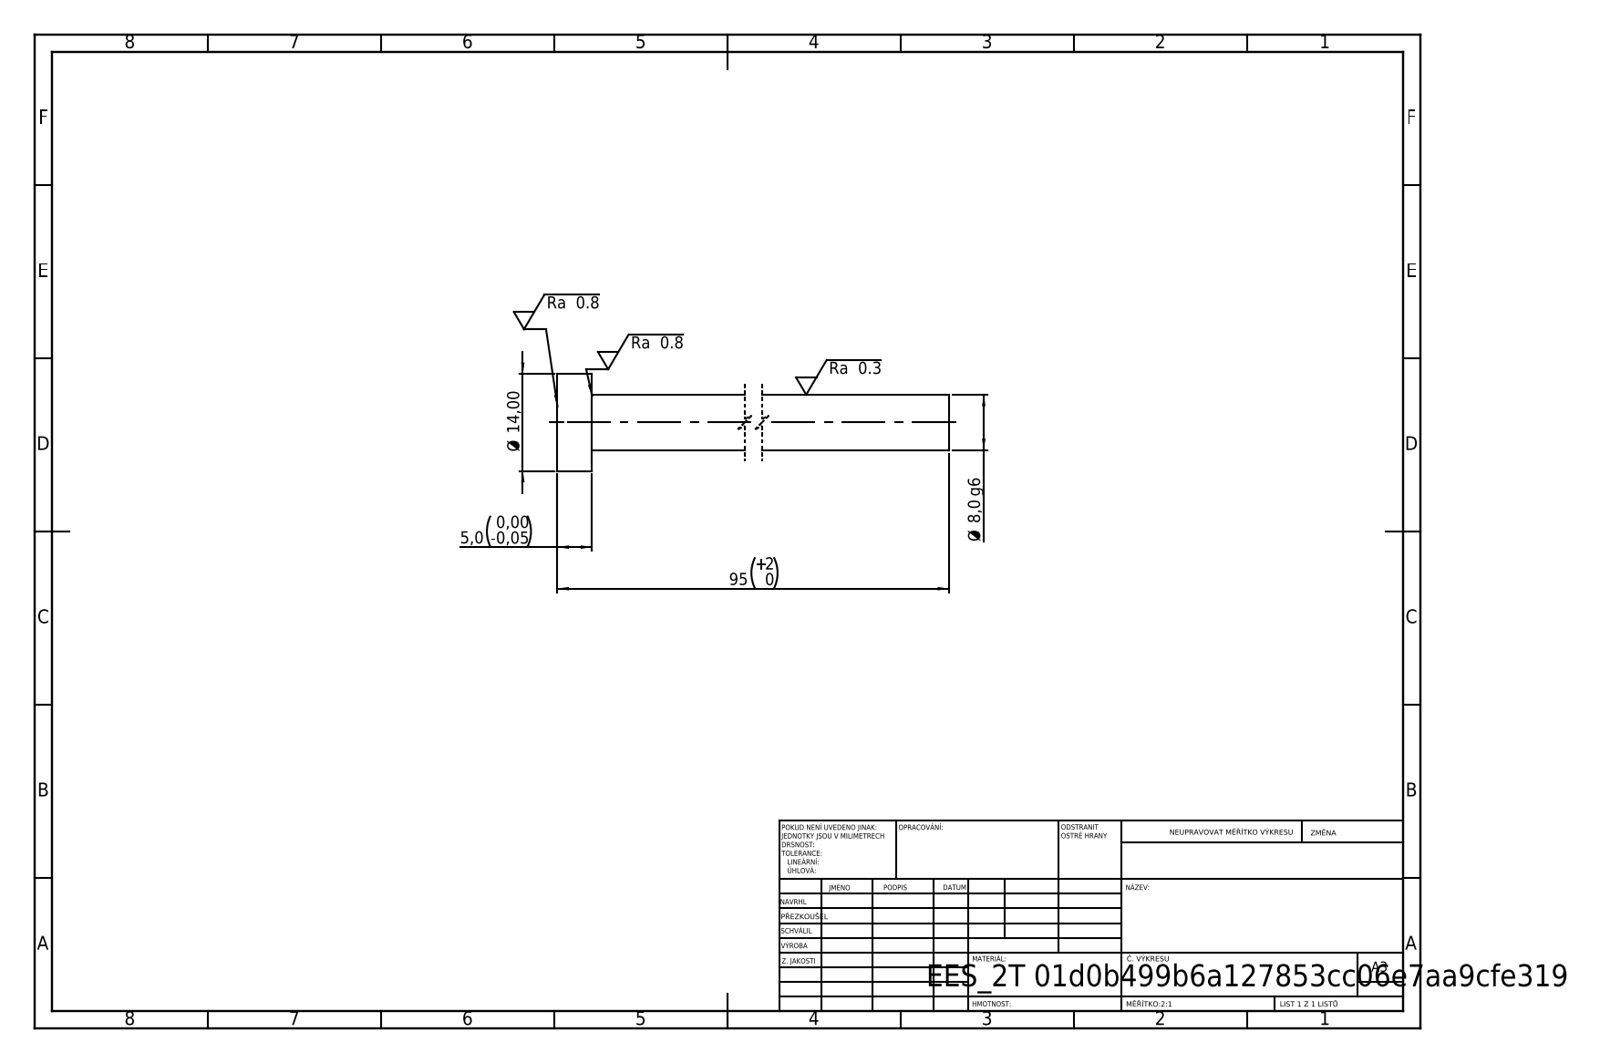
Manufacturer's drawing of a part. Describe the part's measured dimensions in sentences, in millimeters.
Its 3-D file was written by "SolidWorks 2019 (CONFIG_CONTROL_DESIGN)". It is 1 solid with 7 faces: 3 planar, 4 cylindrical and 0 other. Overall it measures 95 by 14 by 14 millimeters. Its volume is 5 294 cubic millimeters and its surface area 2 790 square millimeters. Round bosses or shafts: 1 of diameter 14, 1 of diameter 8. The main face-to-face distances are 5, 95, 90.
